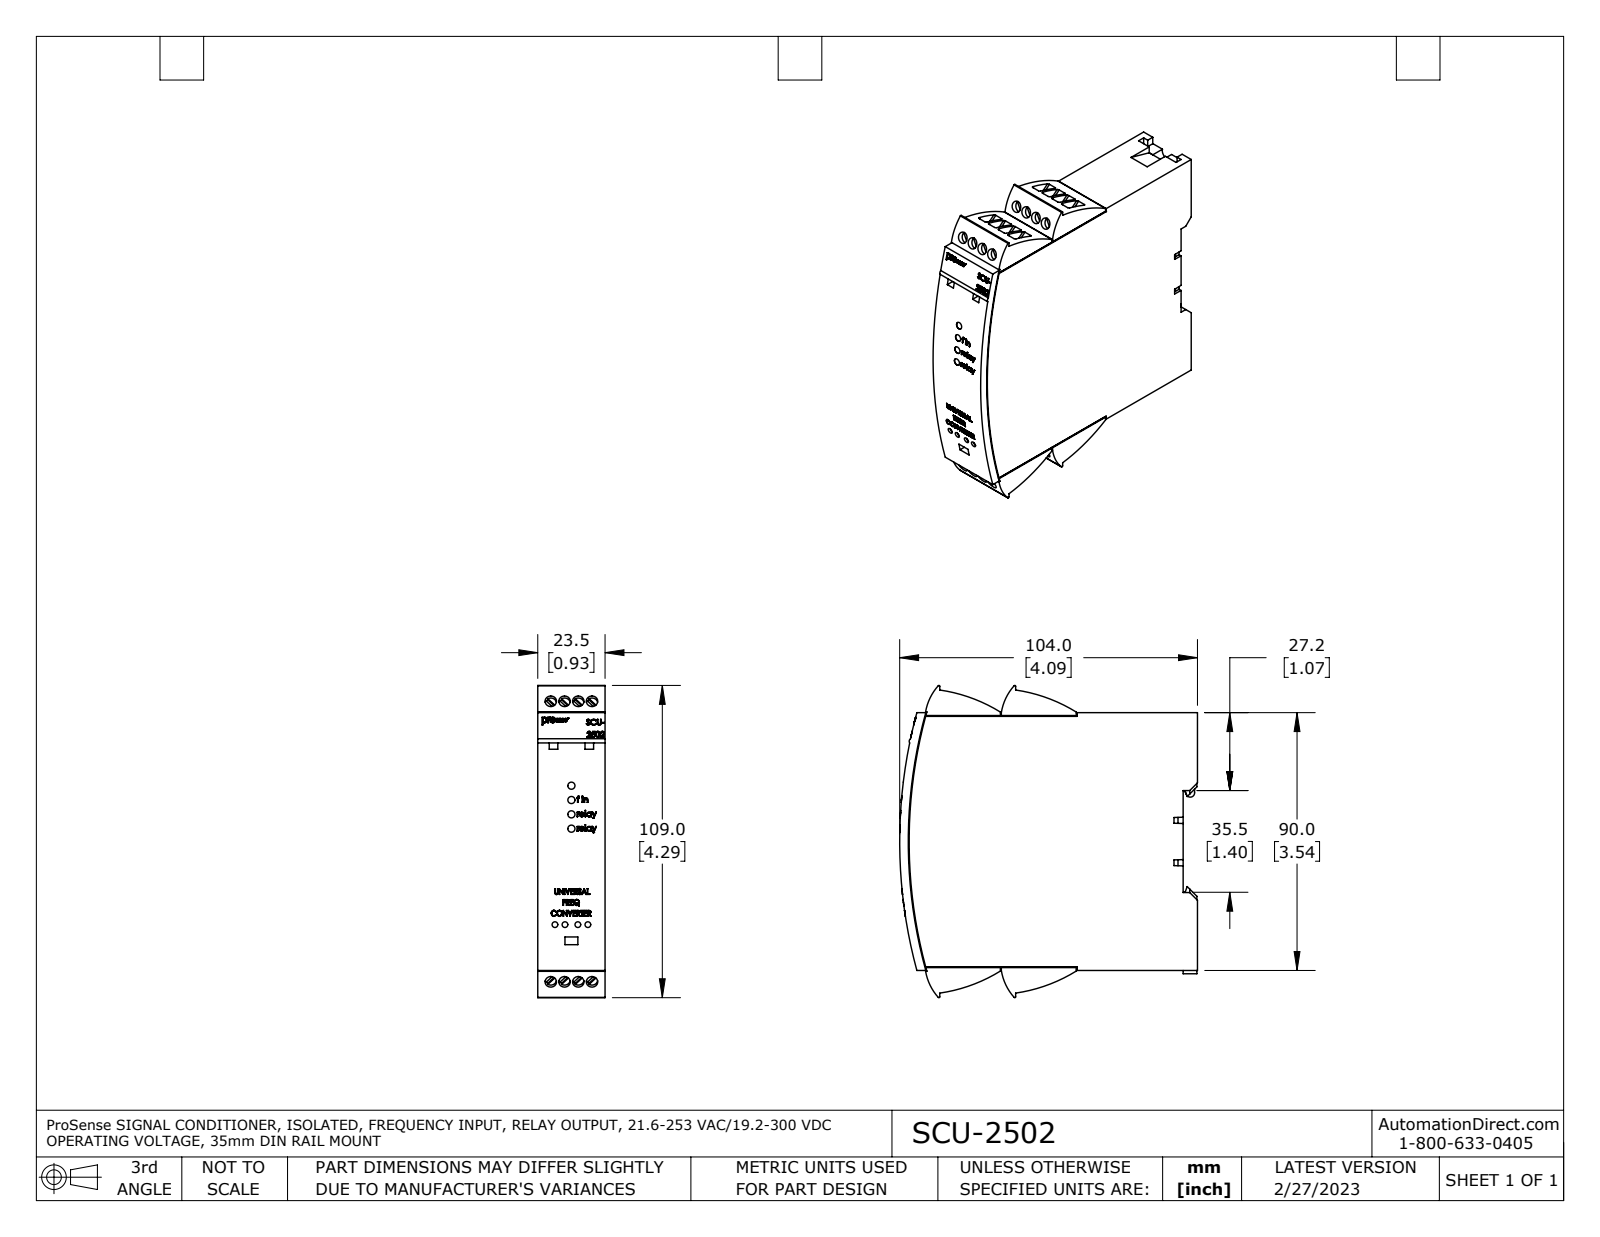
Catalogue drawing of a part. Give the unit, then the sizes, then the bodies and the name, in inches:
Units: inches
Overall size (bounding box): 4.291 × 4.094 × 0.925
Round holes (diameter × count): ⌀0.157 ×16, ⌀0.079 ×4, ⌀0.091 ×4, ⌀0.098 ×4
Round bosses / shafts (diameter × count): ⌀0.079 ×2
Partial cylindrical surfaces — rounded edges, fillets, slot ends (radius × count): R0.02 ×69, R0.012 ×4, R0.04 ×4, R0.726 ×4, R2.175 ×4, R0.059 ×3, R0.098 ×3, R0.03 ×2
Main face-to-face distances: 0.925, 3.543, 0.098, 0.189, 0.187, 0.071, 0.197, 0.118, 0.091, 0.061
Hole centre spacings: 0.189, 0.435, 0.378, 0.391, 0.544, 0.567, 0.689, 0.197
Volume: 13.36 in³ · Surface area: 55.45 in²
Bodies: 3 solids, 1324 faces (750 planar, 253 cylindrical, 321 other)
Part name (STEP PRODUCT): SCU-2502 from 4000_6000_9000 Complete asm nc m1E FP MOD1 fxt
STEP written by: SolidWorks 2021 (AUTOMOTIVE_DESIGN)
